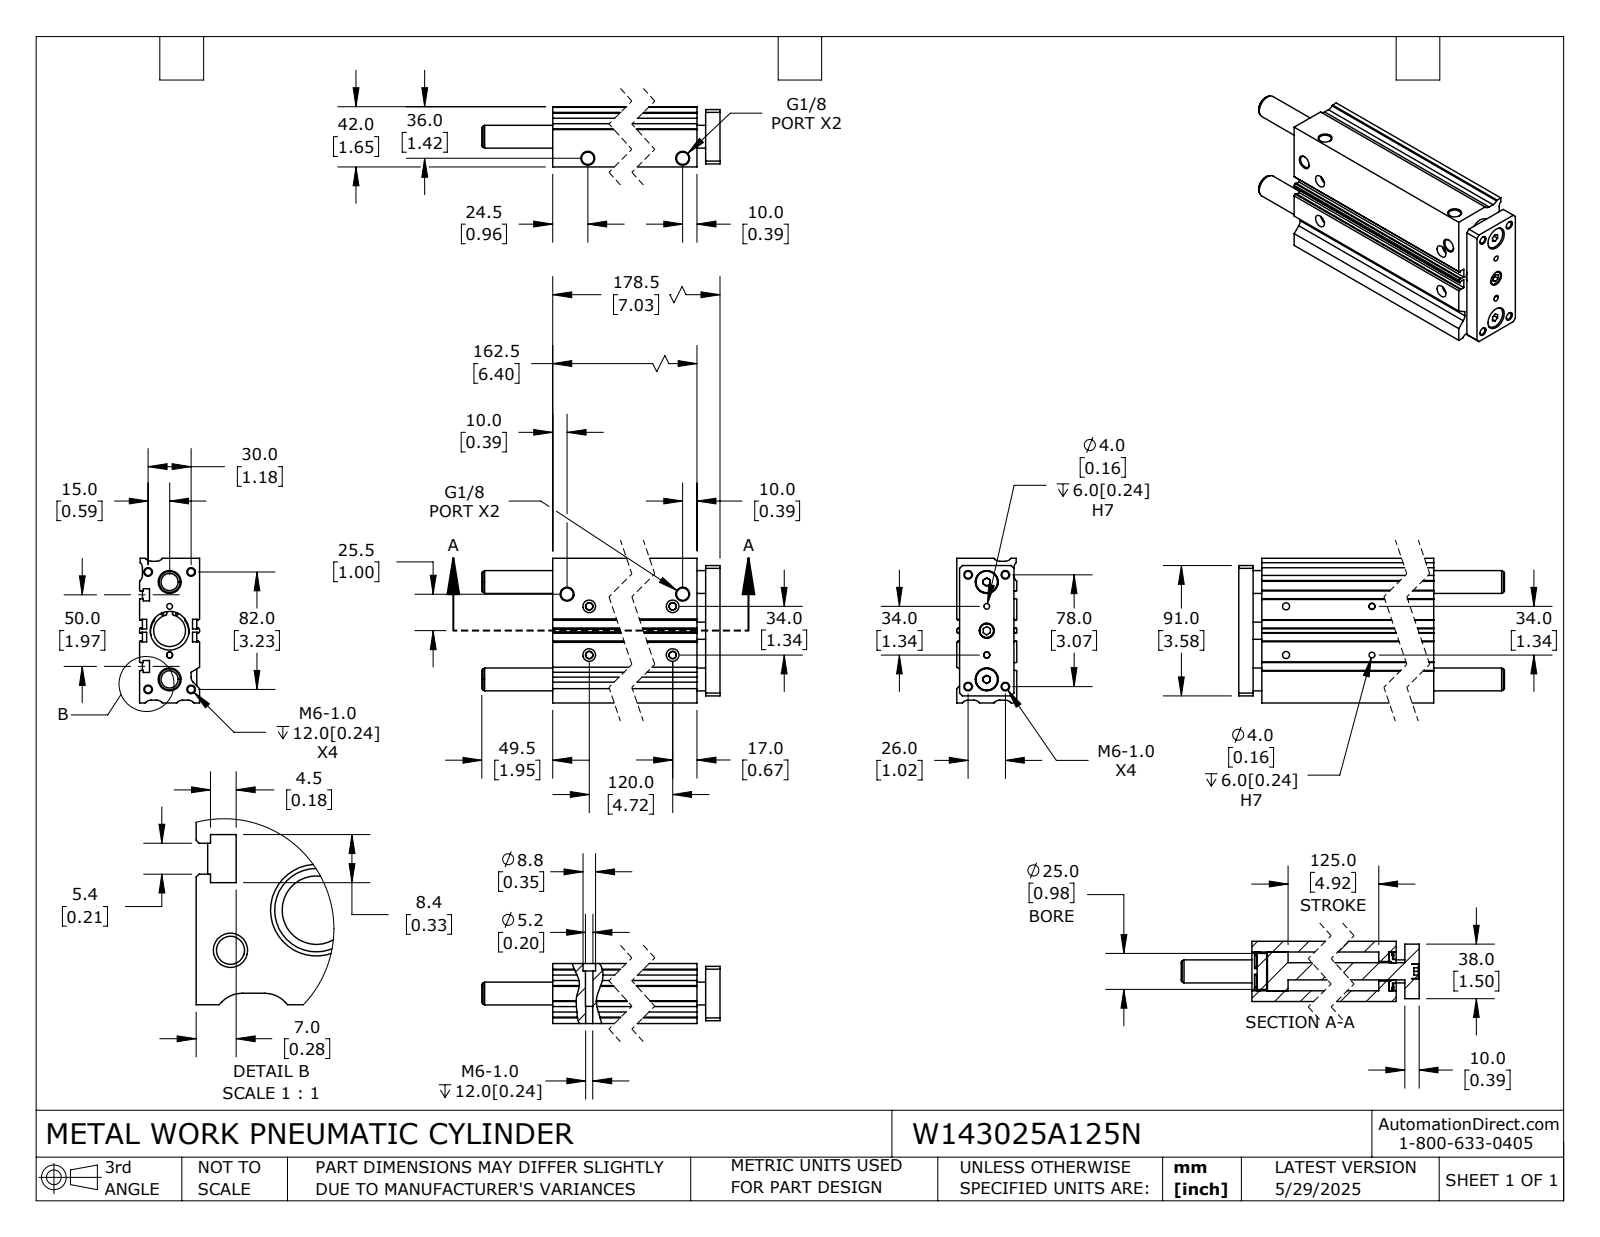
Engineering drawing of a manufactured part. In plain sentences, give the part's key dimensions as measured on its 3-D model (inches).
The part is named "W143025A125N_ROD; W143025A125N; W143025A125N_BODY". Its 3-D file was written by "SolidWorks 2024 (CONFIG_CONTROL_DESIGN)". It is 6 solids with 390 faces: 191 planar, 157 cylindrical and 42 other. Overall it measures 8.976 by 3.976 by 1.654 inches. Its volume is 37.64 cubic inches and its surface area 230 square inches. Round holes: 8 of diameter 0.194, 4 of diameter 0.067, 4 of diameter 0.157, 4 of diameter 0.194, 4 of diameter 0.205, 4 of diameter 0.337, 4 of diameter 0.346, 2 of diameter 0.63, 1 of diameter 0.413, 1 of diameter 0.472, 1 of diameter 0.539, 1 of diameter 0.874. Round bosses or shafts: 2 of diameter 0.61, 1 of diameter 1.063, 1 of diameter 0.984, 1 of diameter 0.65, 1 of diameter 0.394. Partial cylindrical surfaces (rounded edges, fillets, slot ends): 12 of radius 0.039, 9 of radius 0.197, 8 of radius 0.079, 2 of radius 0.524, 1 of radius 0.559. The main face-to-face distances are 1.654, 0.197, 0.079, 1.378, 1.457, 0.118, 0.236, 0.839, 3.976, 2.299. The hole center spacings are 1.339, 0.111, 0.29, 0.5, 0.548, 0.652, 0.669, 0.902.
